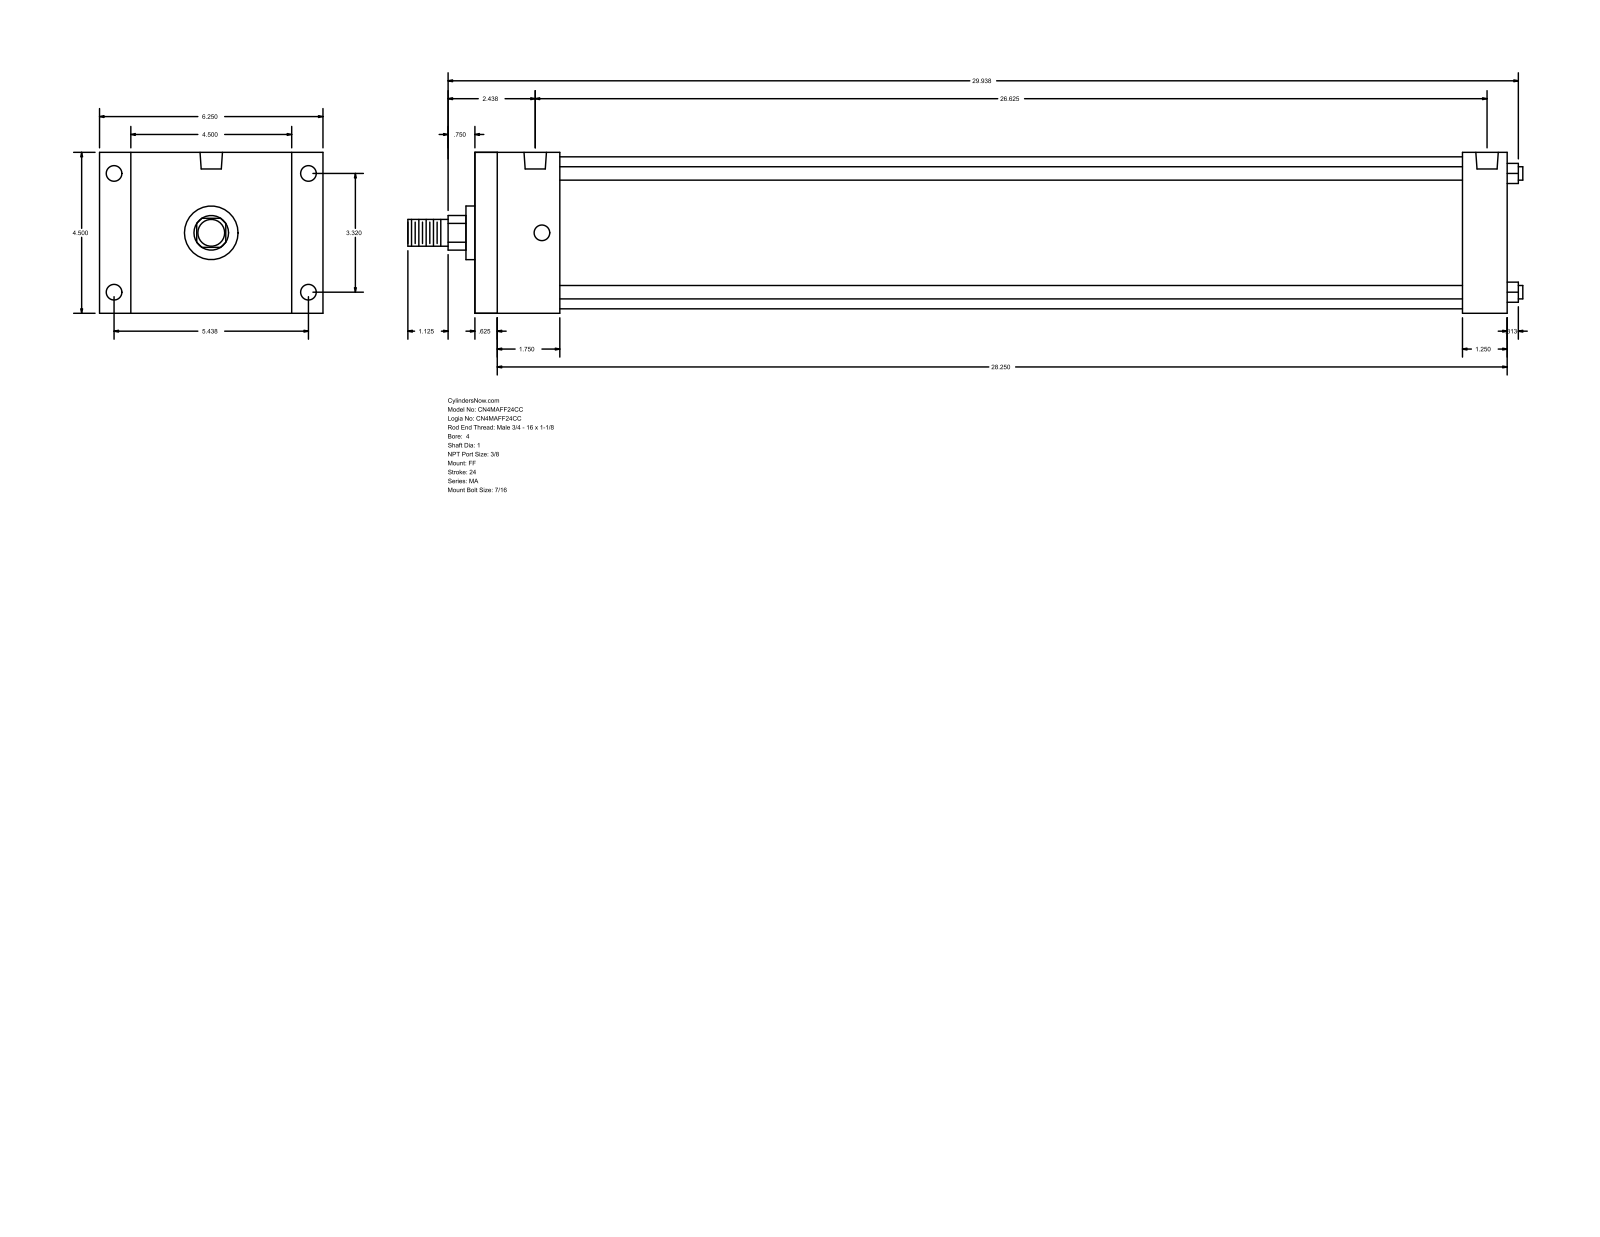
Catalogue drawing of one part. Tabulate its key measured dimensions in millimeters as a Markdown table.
| quantity | value |
| --- | --- |
| part name | MA_FF__0400_1 |
| STEP written by | GSSL Pune (CONFIG_CONTROL_DESIGN) |
| units | millimeters |
| bodies | 0 solids, 92 faces (64 planar, 28 cylindrical, 0 other) |
| overall size | 792.16 × 158.75 × 114.3 |
| round holes (diameter × count) | 11.11 × 8, 15.93 × 2 |
| round bosses / shafts (diameter × count) | 9.53 × 4, 107.95 × 1, 38.1 × 1, 25.4 × 1, 19.05 × 1 |
| partial cylindrical surfaces (radius × count) | 12.29 × 1 |
| main face-to-face distances | 114.3, 733.43, 15.87, 717.56, 22.23, 136.53, 701.68, 685.81, 31.75, 60.33 |
| hole center spacings | 84.32, 138.12, 161.82, 666.75, 4.76, 4.77, 671.51, 671.52 |
